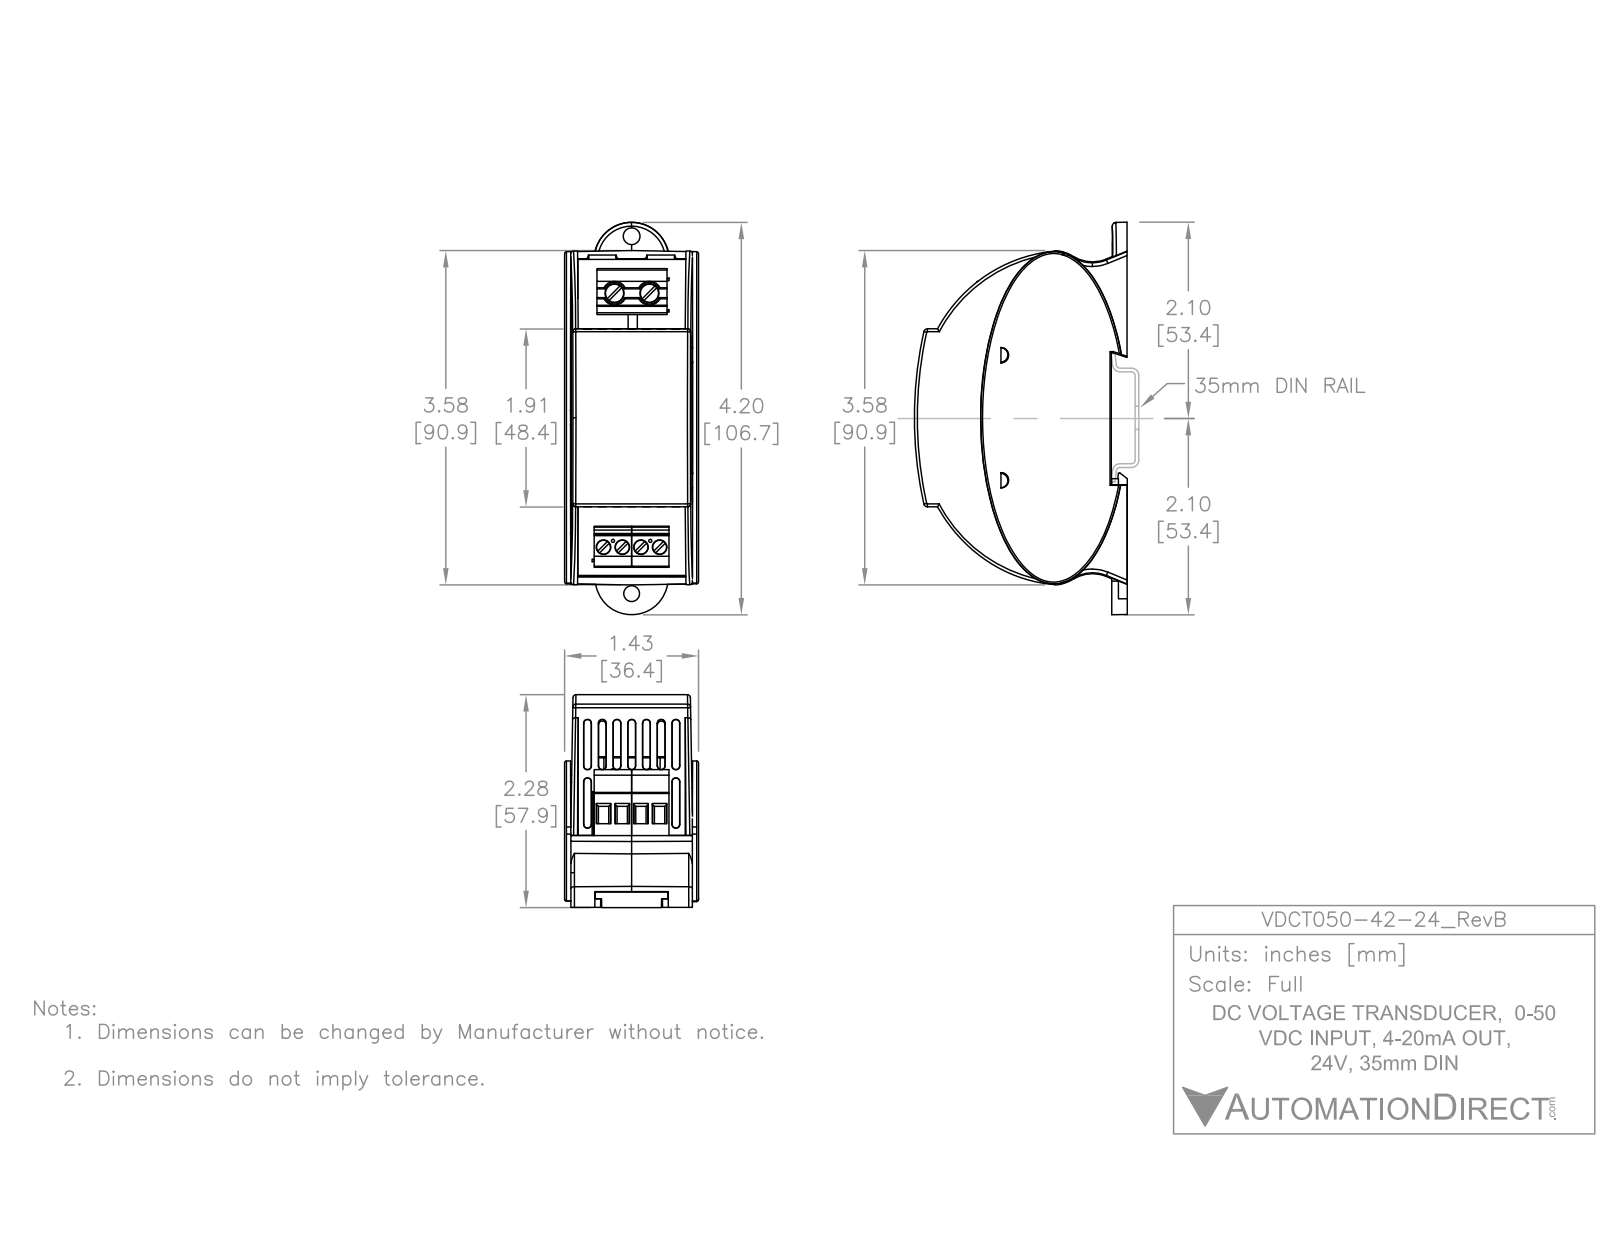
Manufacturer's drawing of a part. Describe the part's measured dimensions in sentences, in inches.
The part is named "VDCT050-42-24". Its 3-D file was written by "SolidWorks 2021 (AUTOMOTIVE_DESIGN)". It is 7 solids with 895 faces: 538 planar, 166 cylindrical and 191 other. Overall it measures 4.203 by 2.298 by 1.46 inches. Its volume is 3.182 cubic inches and its surface area 78.38 square inches. Round holes: 4 of diameter 0.157, 2 of diameter 0.205. Round bosses or shafts: 6 of diameter 0.051, 4 of diameter 0.15, 3 of diameter 0.018, 2 of diameter 0.197. Partial cylindrical surfaces (rounded edges, fillets, slot ends): 29 of radius 0.006, 12 of radius 0.039, 11 of radius 0.02, 8 of radius 0.008, 8 of radius 0.026, 5 of radius 0.012, 4 of radius 0.032, 4 of radius 0.04. The main face-to-face distances are 1.435, 0.064, 0.436, 0.5, 1.262, 1.265, 0.702, 0.266, 0.766, 1.906. The hole center spacings are 0.2, 0.4, 0.375, 0.6, 2.719, 2.719, 2.72, 2.72.
